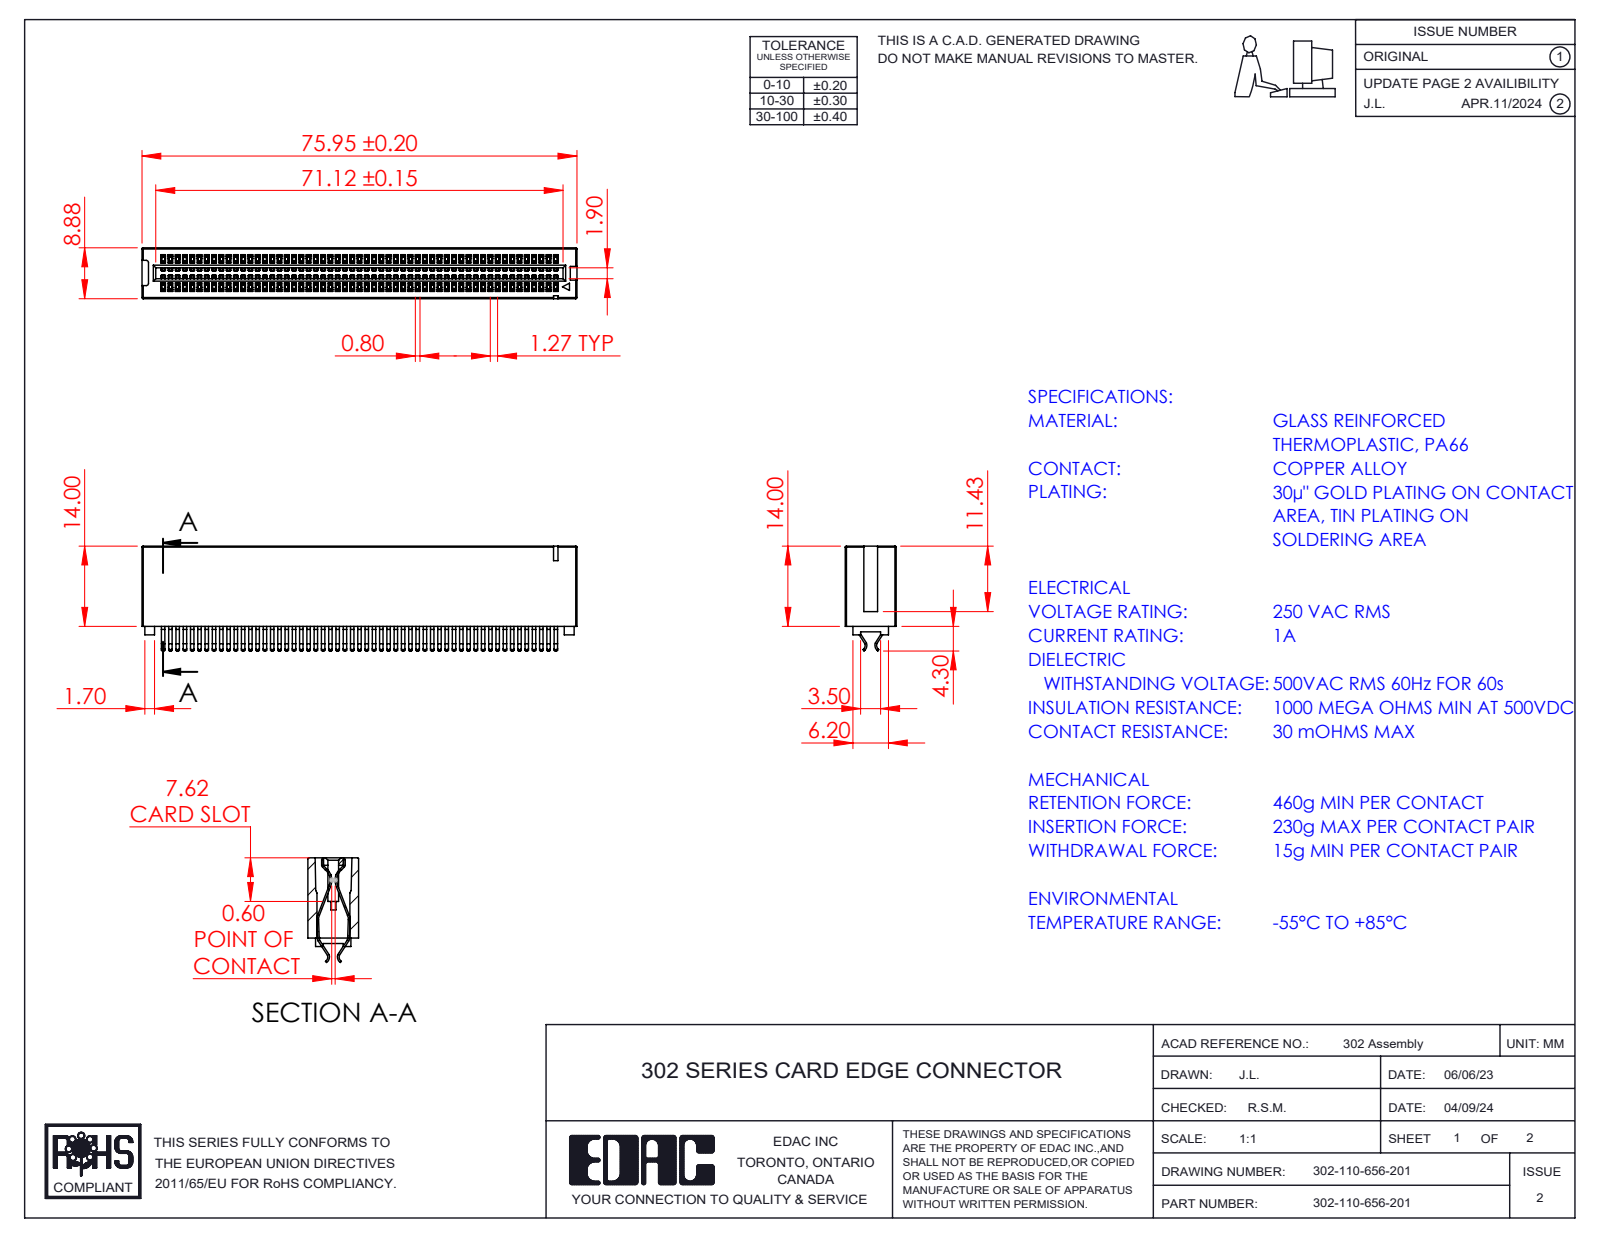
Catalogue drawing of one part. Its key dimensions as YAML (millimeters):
part_name: "HSG_Vertical HSG; 302-110-656-201; Contact_302-290-X56"
step_written_by: "SolidWorks 2023 (CONFIG_CONTROL_DESIGN)"
units: millimeters
bodies: {solids: 111, faces: 5291, planar: 3514, cylindrical: 1773, other: 4}
overall_size: [75.95, 18.3, 8.88]
volume: 5808
surface_area: 16679
partial_cylinders:
  - {radius: 0.2, count: 338}
  - {radius: 0.11, count: 2}
  - {radius: 0.4, count: 2}
  - {radius: 0.41, count: 2}
  - {radius: 0.93, count: 2}
  - {radius: 1.05, count: 2}
  - {radius: 1.23, count: 2}
  - {radius: 1.25, count: 2}
face_to_face_distances: [8.88, 1.27, 2.54, 3.81, 5.08, 7.62, 6.35, 8.89, 10.16, 1.9]
